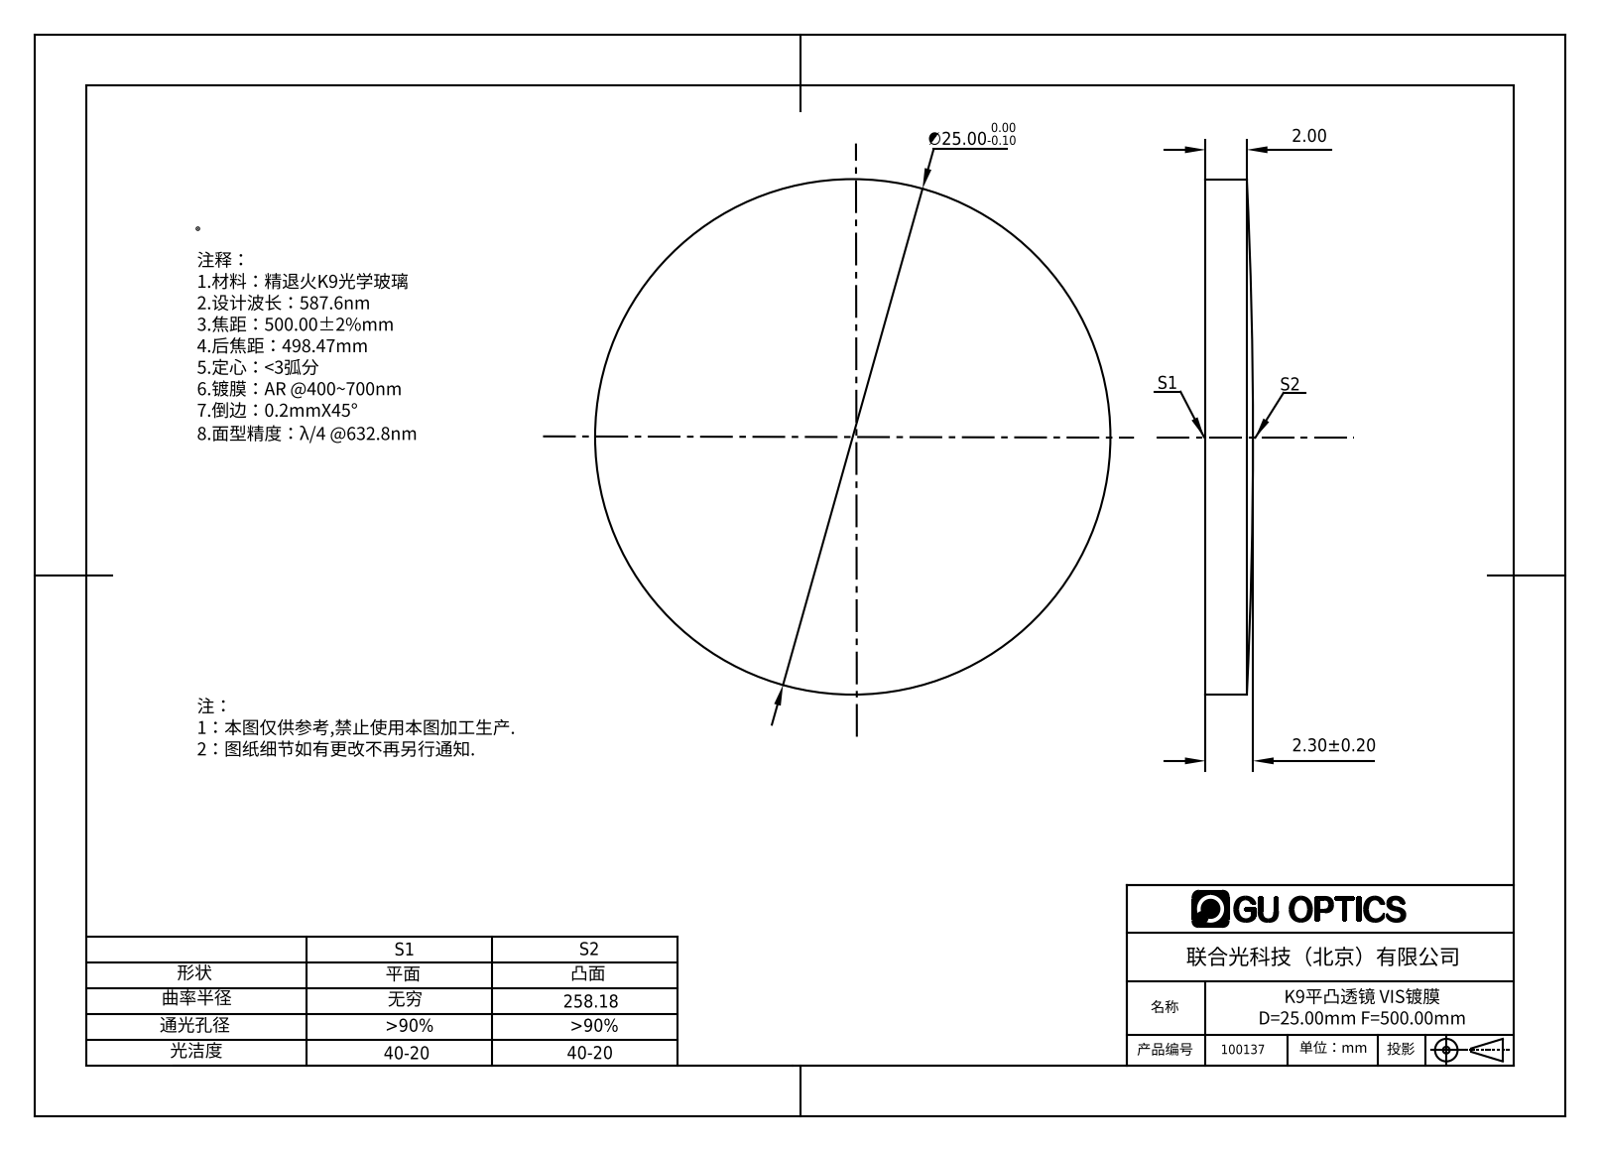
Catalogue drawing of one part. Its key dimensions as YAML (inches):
part_name: "100137"
step_written_by: "SolidWorks 2016 (AUTOMOTIVE_DESIGN)"
units: inches
bodies: {solids: 1, faces: 5, planar: 1, cylindrical: 2, other: 2}
overall_size: [0.984, 0.984, 0.091]
volume: 0.064
surface_area: 1.765
round_bosses_or_shafts:
  - {diameter: 0.984, count: 1}
